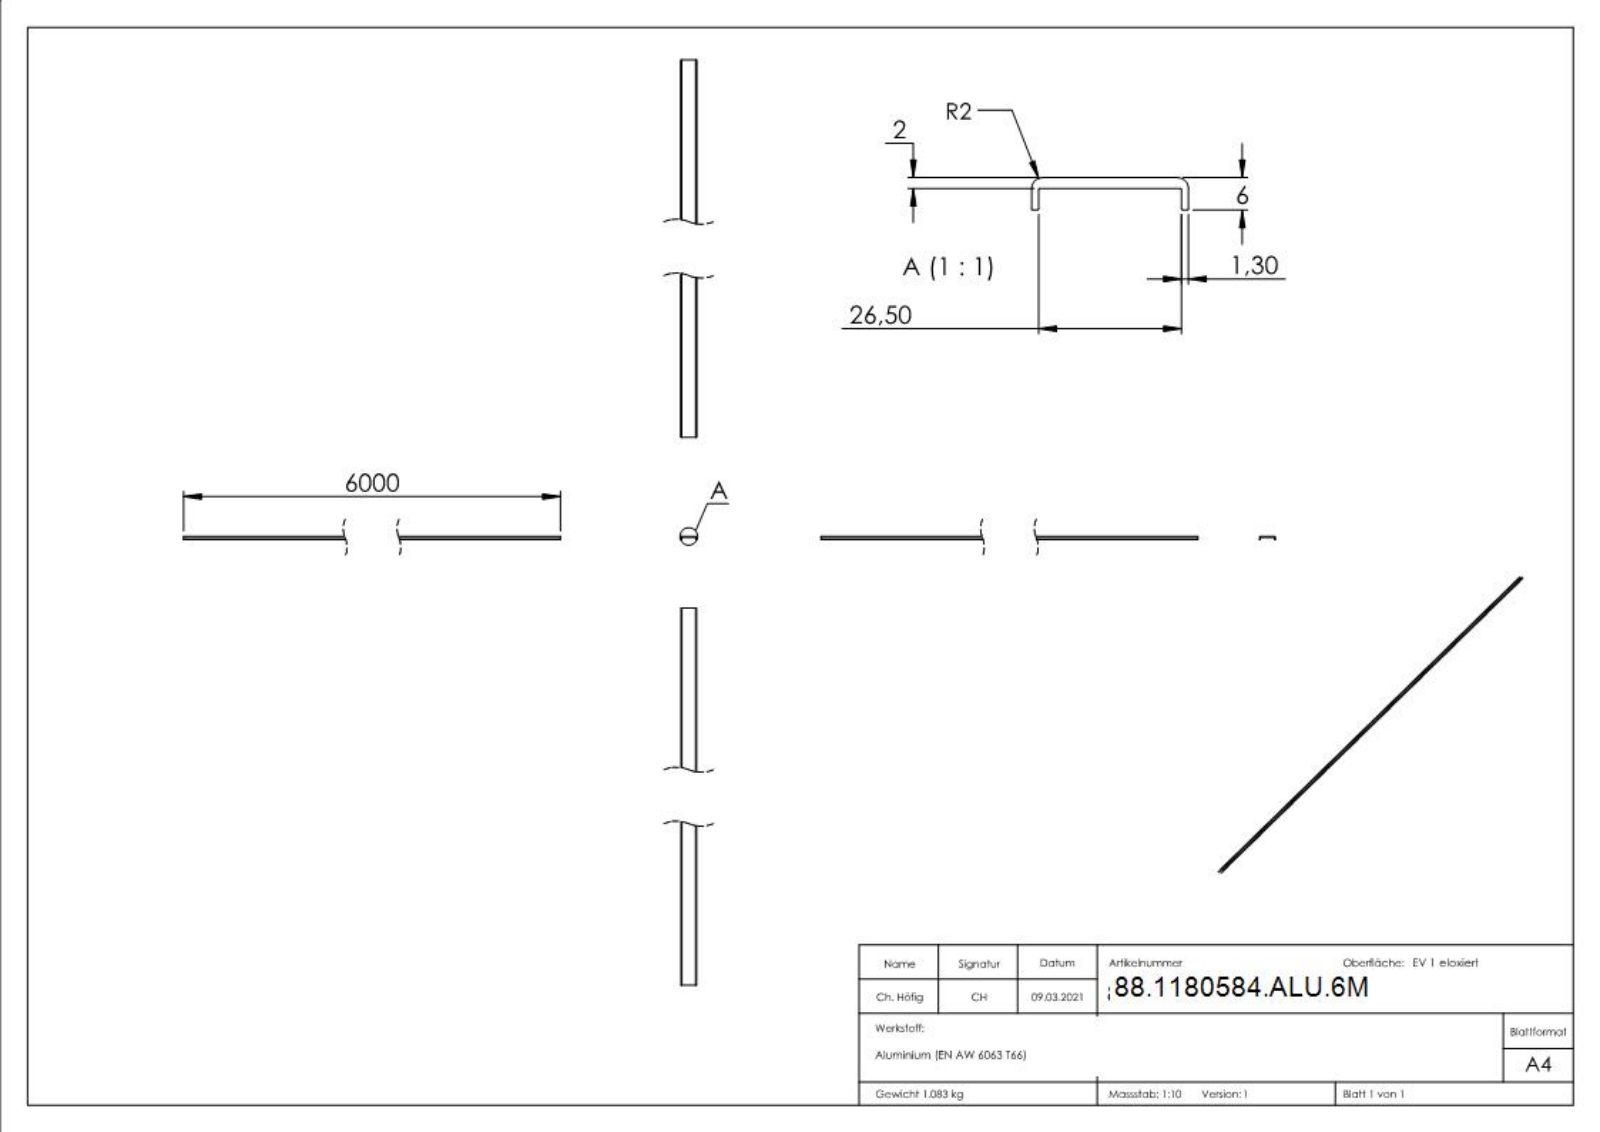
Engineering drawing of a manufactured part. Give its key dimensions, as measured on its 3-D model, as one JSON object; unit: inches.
{"part_name": "80584-ALU-6M", "step_written_by": "SolidWorks 2018 (CONFIG_CONTROL_DESIGN)", "units": "inches", "bodies": {"solids": 1, "faces": 342, "planar": 195, "cylindrical": 8, "other": 139}, "overall_size": [236.22, 1.146, 0.236], "volume_in3": 24.48, "surface_area_in2": 706.7, "partial_cylinders_radius": [[0.008, 6], [0.079, 2]], "face_to_face_distances": [0.079, 0.051, 1.094, 1.146, 1.043, 0.236, 0.157, 236.22, 0.161, 0.075]}
